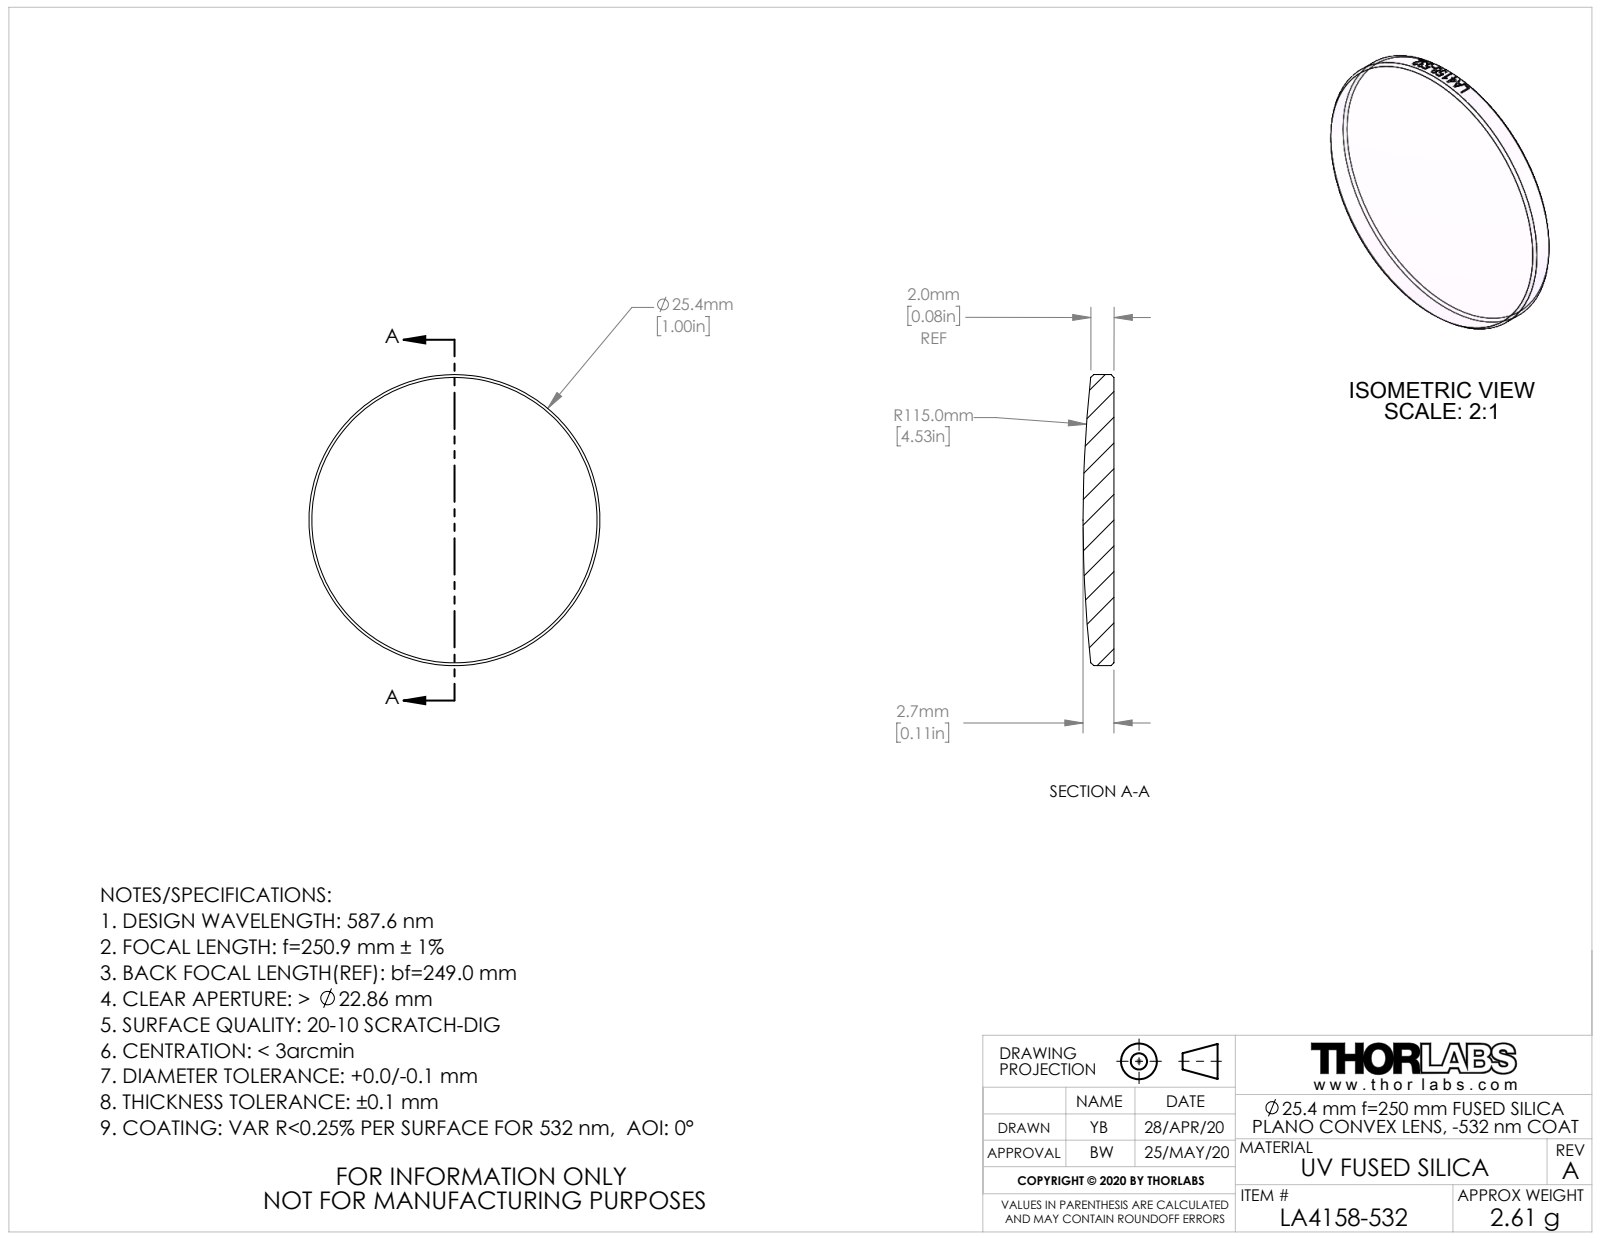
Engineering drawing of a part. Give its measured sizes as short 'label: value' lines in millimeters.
name: CTN015733-E0W
written by: SolidWorks 2018 (AUTOMOTIVE_DESIGN)
unit: mm
bodies: 1 solid, 28 faces (1 planar, 21 cylindrical, 6 other)
size: 25.4 × 25.4 × 2.7
volume: 1 186 mm³; area: 1 152 mm²
bosses: 1× ⌀25.4
